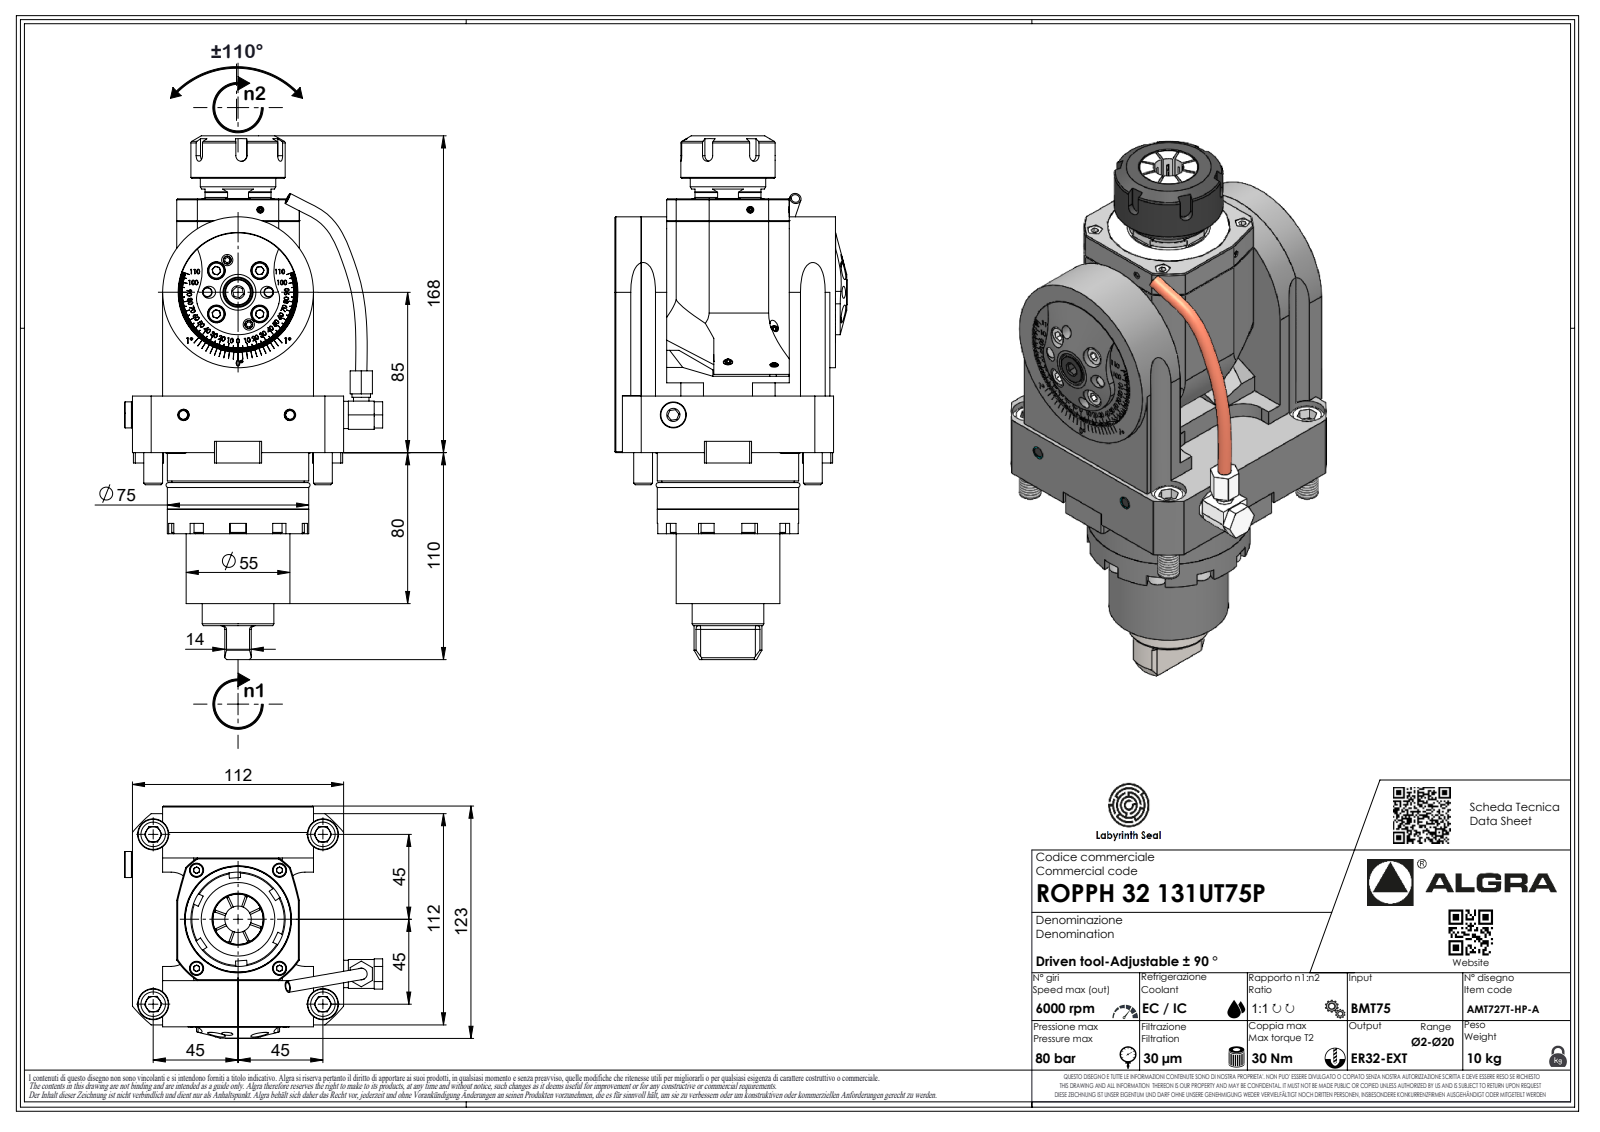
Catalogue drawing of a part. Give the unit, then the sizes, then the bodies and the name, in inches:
Units: inches
Overall size (bounding box): 10.93 × 5.224 × 4.843
Round holes (diameter × count): ⌀0.083 ×1, ⌀0.197 ×1
Round bosses / shafts (diameter × count): ⌀3.15 ×1, ⌀2.953 ×1, ⌀2.764 ×1, ⌀2.165 ×1, ⌀1.969 ×1, ⌀1.575 ×1, ⌀1.496 ×1, ⌀0.571 ×1
Partial cylindrical surfaces — rounded edges, fillets, slot ends (radius × count): R0.171 ×10, R0.013 ×7, R0.02 ×7, R0.146 ×7, R0.079 ×6, R0.157 ×6, R0.118 ×5, R0.472 ×4
Main face-to-face distances: 0.925, 3.484, 0.63, 2.559, 1.181, 3.78, 3.15, 0.295, 2.854, 0.965
Volume: 90.07 in³ · Surface area: 194.1 in²
Bodies: 1 solid, 656 faces (433 planar, 105 cylindrical, 118 other)
Part name (STEP PRODUCT): ROPPH32131UT75P
STEP written by: SolidWorks 2023 (AUTOMOTIVE_DESIGN)
